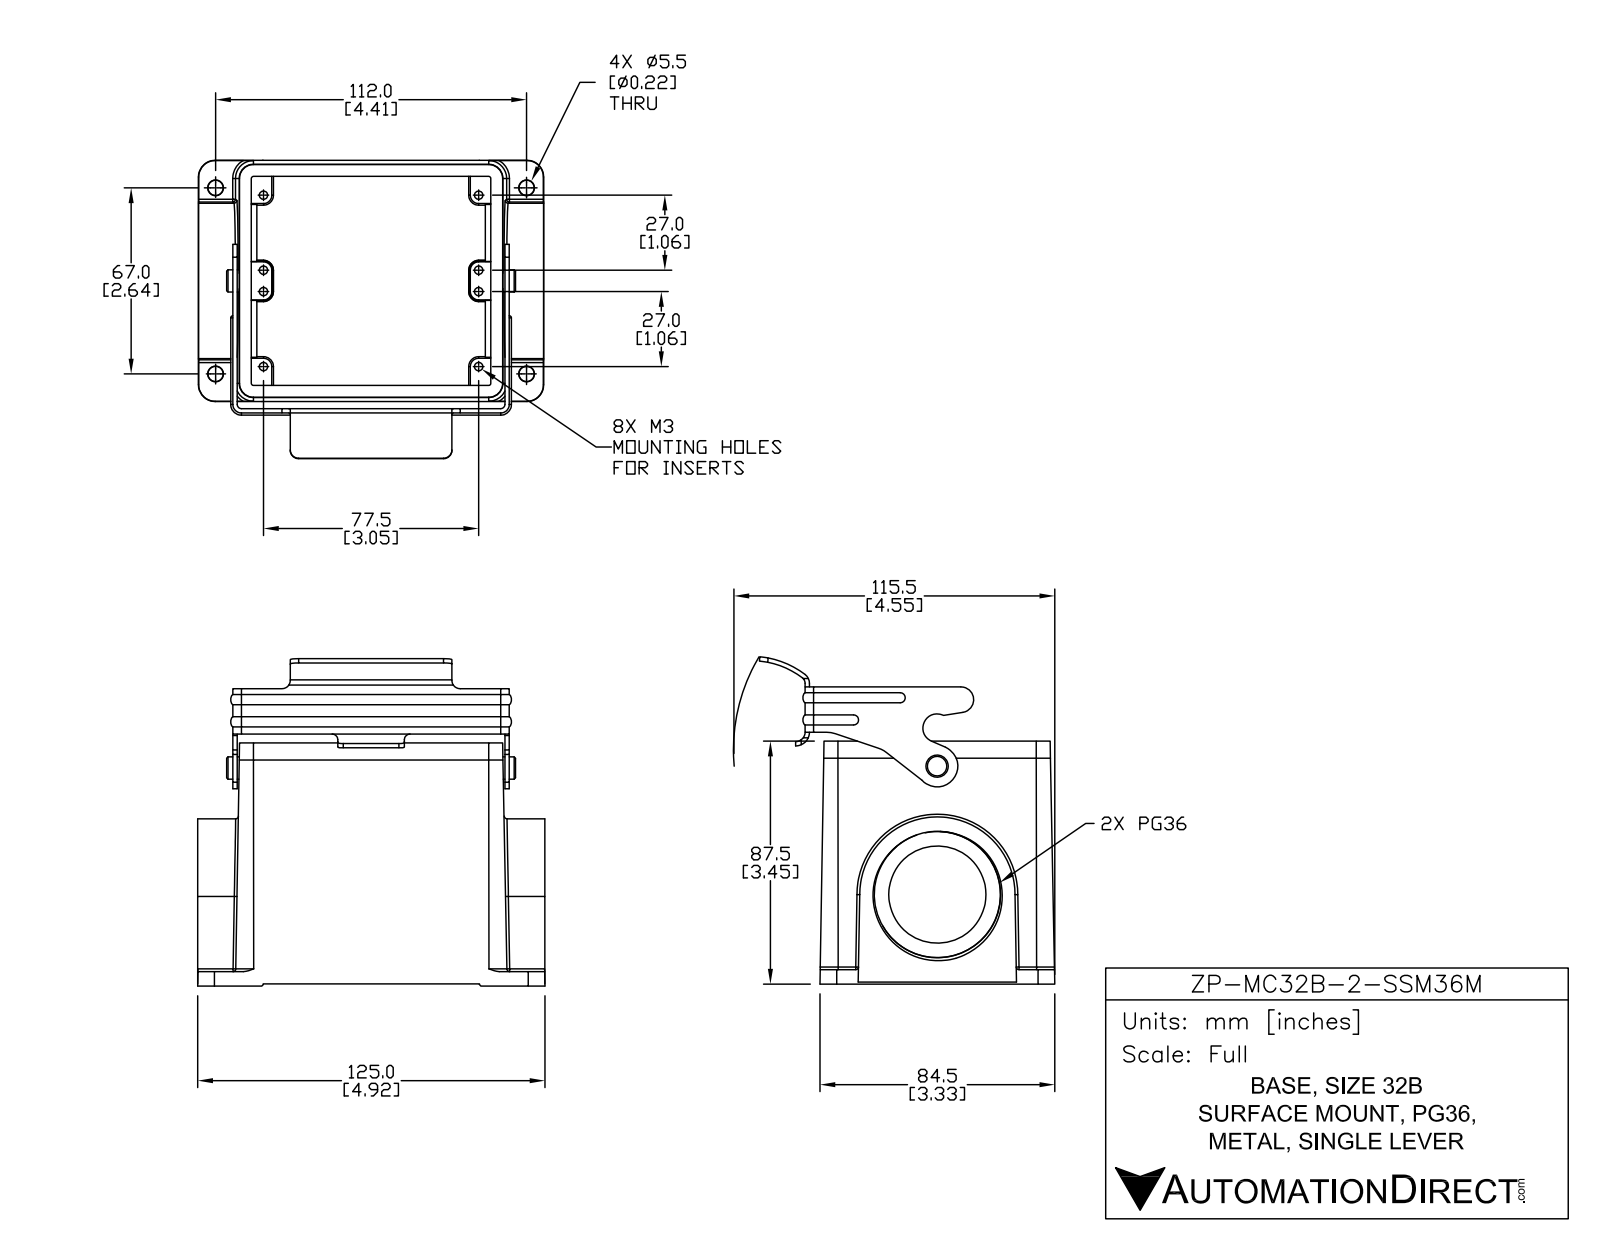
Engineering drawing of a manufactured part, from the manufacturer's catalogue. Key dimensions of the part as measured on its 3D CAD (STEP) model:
Part name (STEP PRODUCT): ZP-MC32B-2-SSM36M
STEP written by: SolidWorks 2014 (AUTOMOTIVE_DESIGN)
Units: millimetres
Bodies: 1 solid, 317 faces (111 planar, 140 cylindrical, 66 other)
Overall size (bounding box): 124.33 × 119.98 × 106.14
Volume: 259 406 mm³ · Surface area: 99 643 mm²
Round holes (diameter × count): ⌀3 ×8, ⌀35 ×1, ⌀45.5 ×1
Round bosses / shafts (diameter × count): ⌀8 ×1
Partial cylindrical surfaces — rounded edges, fillets, slot ends (radius × count): R1 ×8, R0.75 ×4, R2 ×4, R3 ×4, R1.5 ×2, R3.06 ×2, R10 ×2, R3.38 ×1
Main face-to-face distances: 72.95, 7.75, 0.75, 8.5, 1.56, 21, 103.3, 13.95, 110.35, 7.05
Hole centre spacings: 27, 34.7, 77.5, 82.07, 84.91, 7.7, 61.7, 77.88
